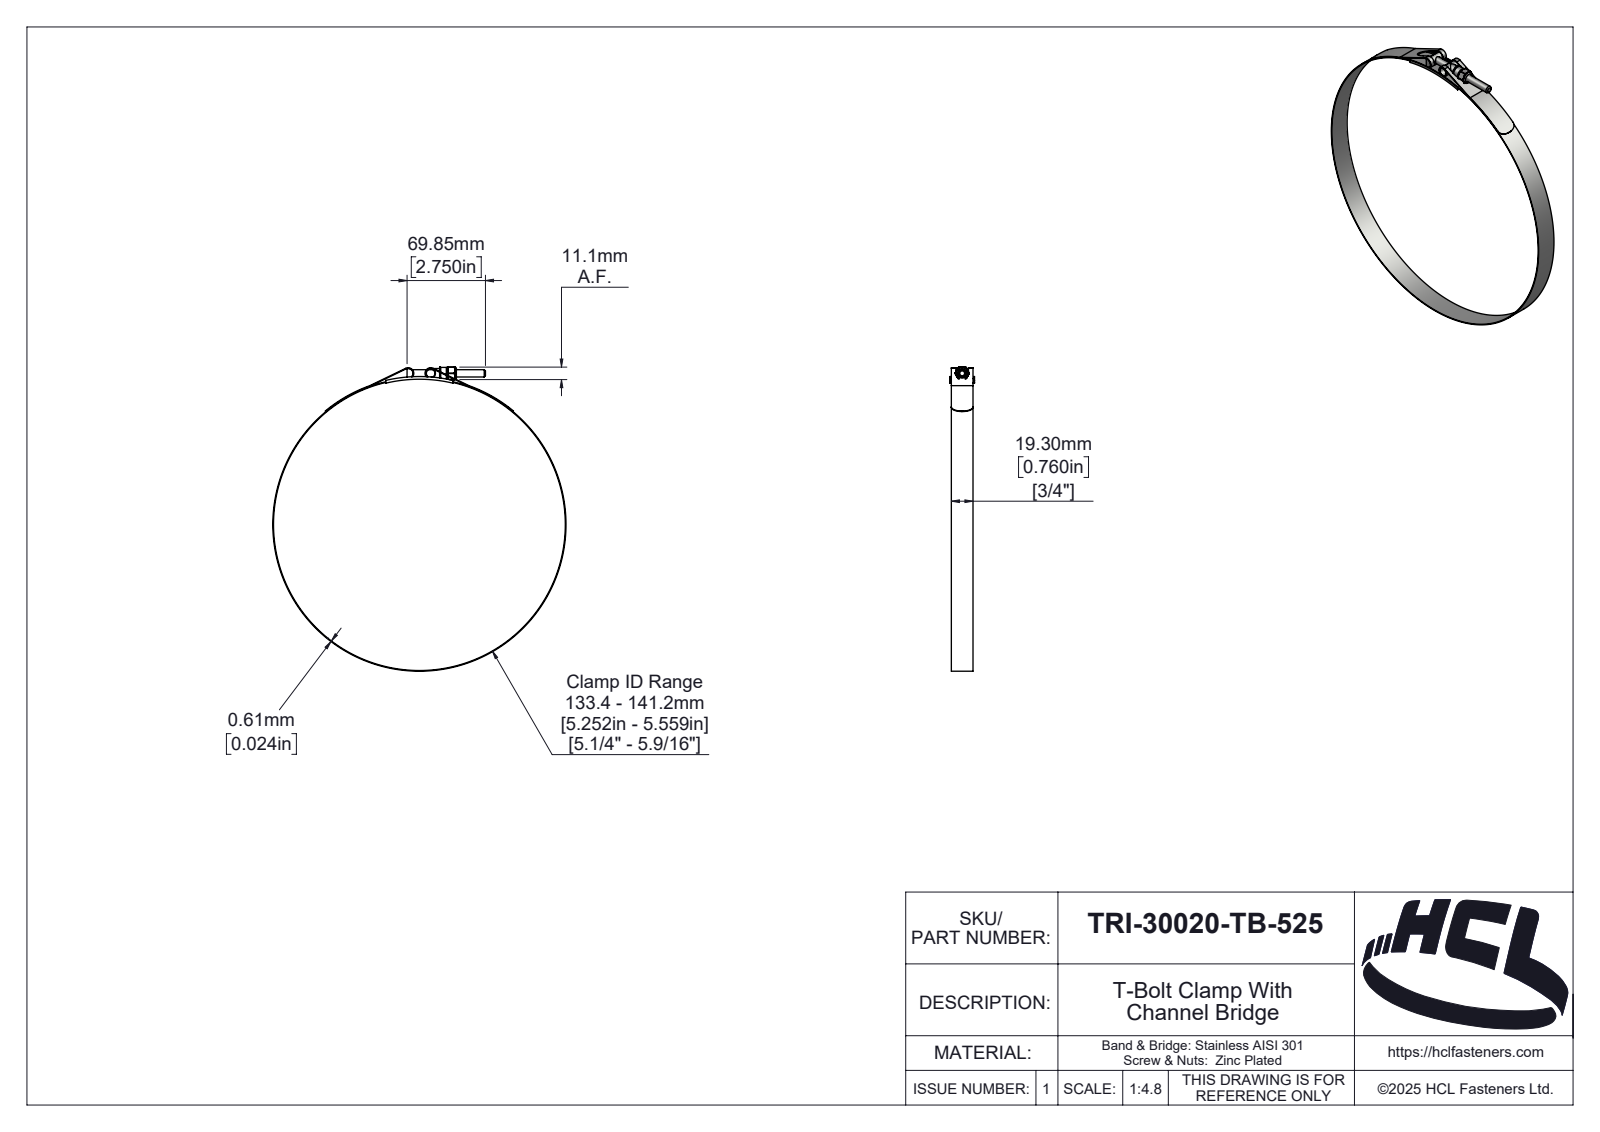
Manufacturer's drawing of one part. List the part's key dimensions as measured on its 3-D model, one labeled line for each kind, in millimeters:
Part name (STEP PRODUCT): TRI-30020-TB-525
STEP written by: SolidWorks 2025 (AUTOMOTIVE_DESIGN)
Units: millimetres
Bodies: 6 solids, 330 faces (44 planar, 122 cylindrical, 164 other)
Overall size (bounding box): 270.96 × 261.22 × 22
Volume: 16 384 mm³ · Surface area: 45 772 mm²
Round holes (diameter × count): ⌀5.4 ×1, ⌀6.35 ×1, ⌀6.5 ×1, ⌀7.58 ×1, ⌀260 ×1
Round bosses / shafts (diameter × count): ⌀8.58 ×2, ⌀261.22 ×1, ⌀10.58 ×1
Partial cylindrical surfaces — rounded edges, fillets, slot ends (radius × count): R0.39 ×6, R0.5 ×2, R4.39 ×2, R5 ×2, R0.59 ×1, R2.42 ×1, R3.03 ×1, R3.19 ×1
Main face-to-face distances: 0.61, 19.3, 1.35, 20.65, 0.74, 21.39, 20.04, 22, 20.78, 36
Hole centre spacings: 135
